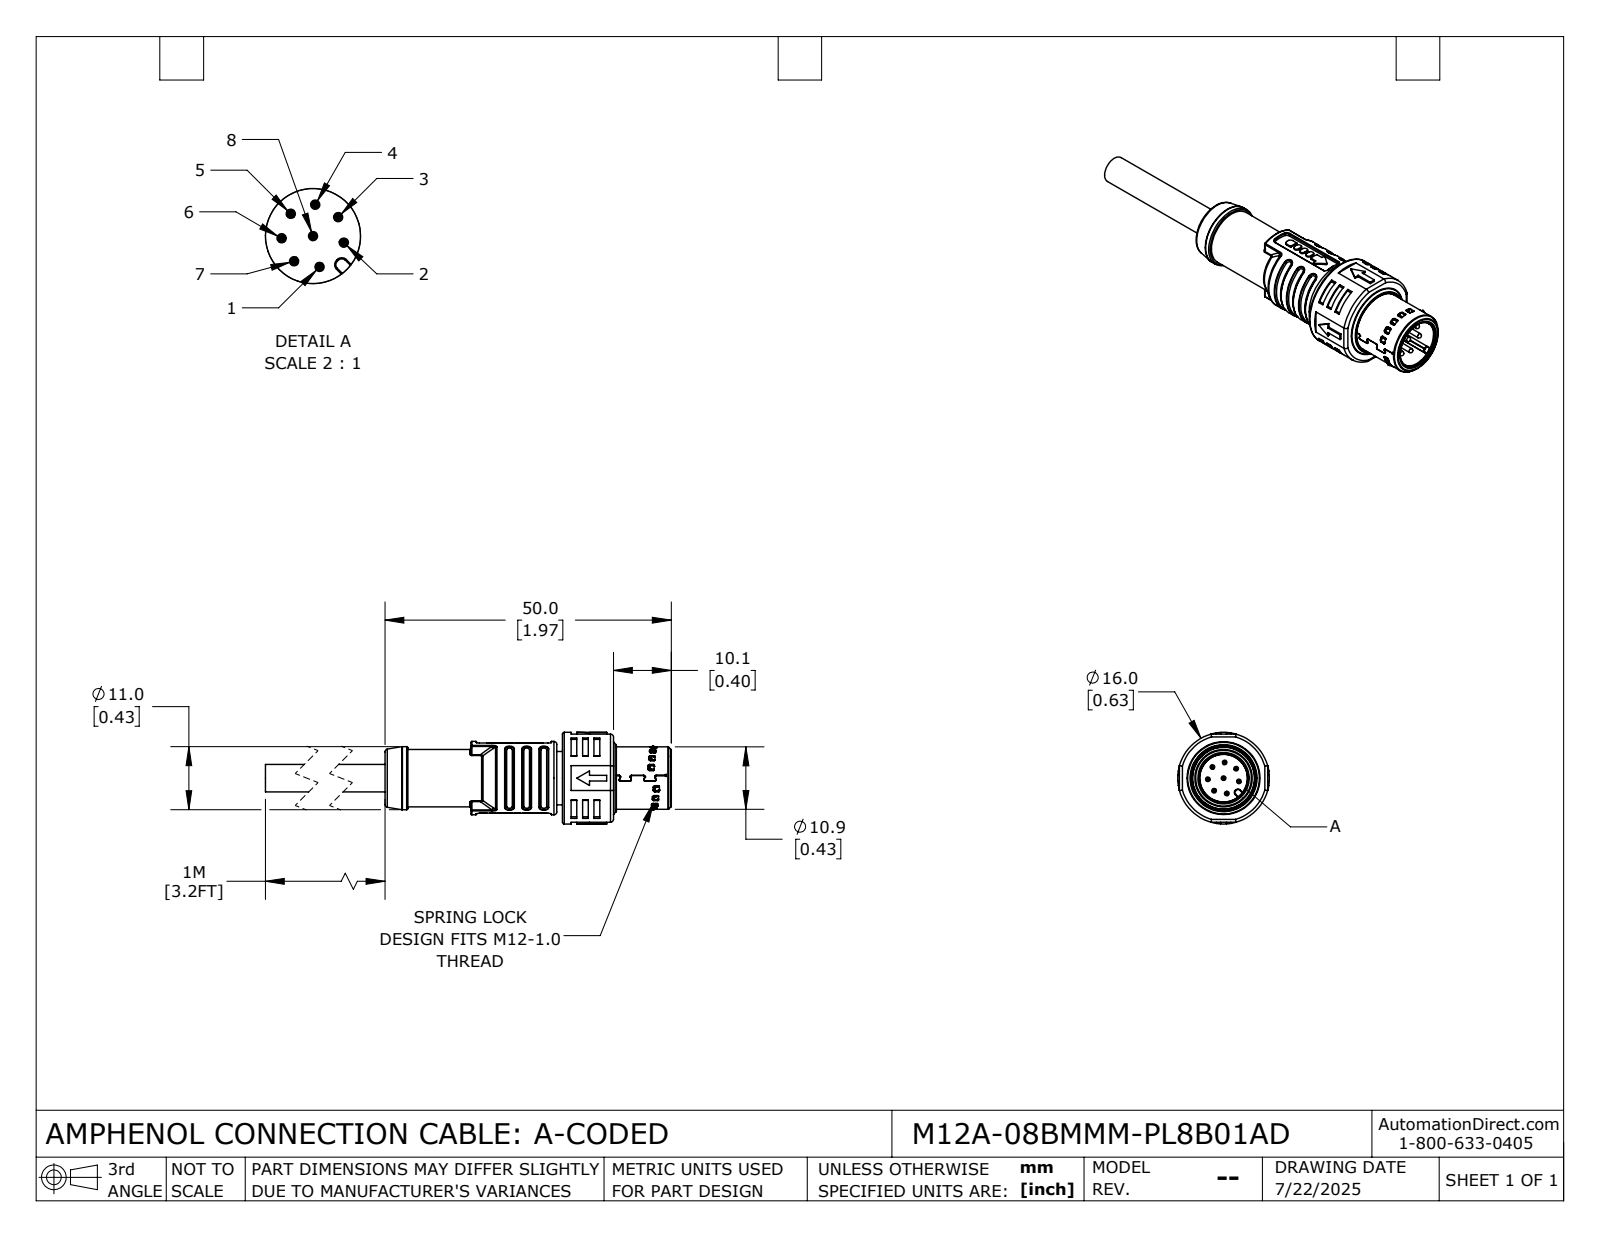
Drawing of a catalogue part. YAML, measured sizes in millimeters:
part_name: "M12A-08BMMM-PL8B01AD"
step_written_by: "SolidWorks 2024 (CONFIG_CONTROL_DESIGN)"
units: millimeters
bodies: {solids: 1, faces: 2027, planar: 880, cylindrical: 644, other: 503}
overall_size: [75, 16, 16]
volume: 5223
surface_area: 5723
round_holes:
  - {diameter: 8.3, count: 1}
  - {diameter: 9, count: 1}
  - {diameter: 10.15, count: 1}
  - {diameter: 10.5, count: 1}
  - {diameter: 10.9, count: 1}
  - {diameter: 11.5, count: 1}
  - {diameter: 11.8, count: 1}
  - {diameter: 14.2, count: 1}
round_bosses_or_shafts:
  - {diameter: 0.8, count: 8}
  - {diameter: 16, count: 1}
  - {diameter: 14.1, count: 1}
  - {diameter: 12.8, count: 1}
  - {diameter: 12.4, count: 1}
  - {diameter: 11, count: 1}
  - {diameter: 10.45, count: 1}
  - {diameter: 10.4, count: 1}
partial_cylinders:
  - {radius: 0.2, count: 114}
  - {radius: 0.25, count: 66}
  - {radius: 0.3, count: 64}
  - {radius: 0.15, count: 44}
  - {radius: 0.5, count: 38}
  - {radius: 0.13, count: 12}
  - {radius: 0.7, count: 11}
  - {radius: 0.1, count: 10}
face_to_face_distances: [1, 10.1, 8.6, 8.9, 2.5, 1.5, 1.2, 32.5, 15.4, 41.1]
